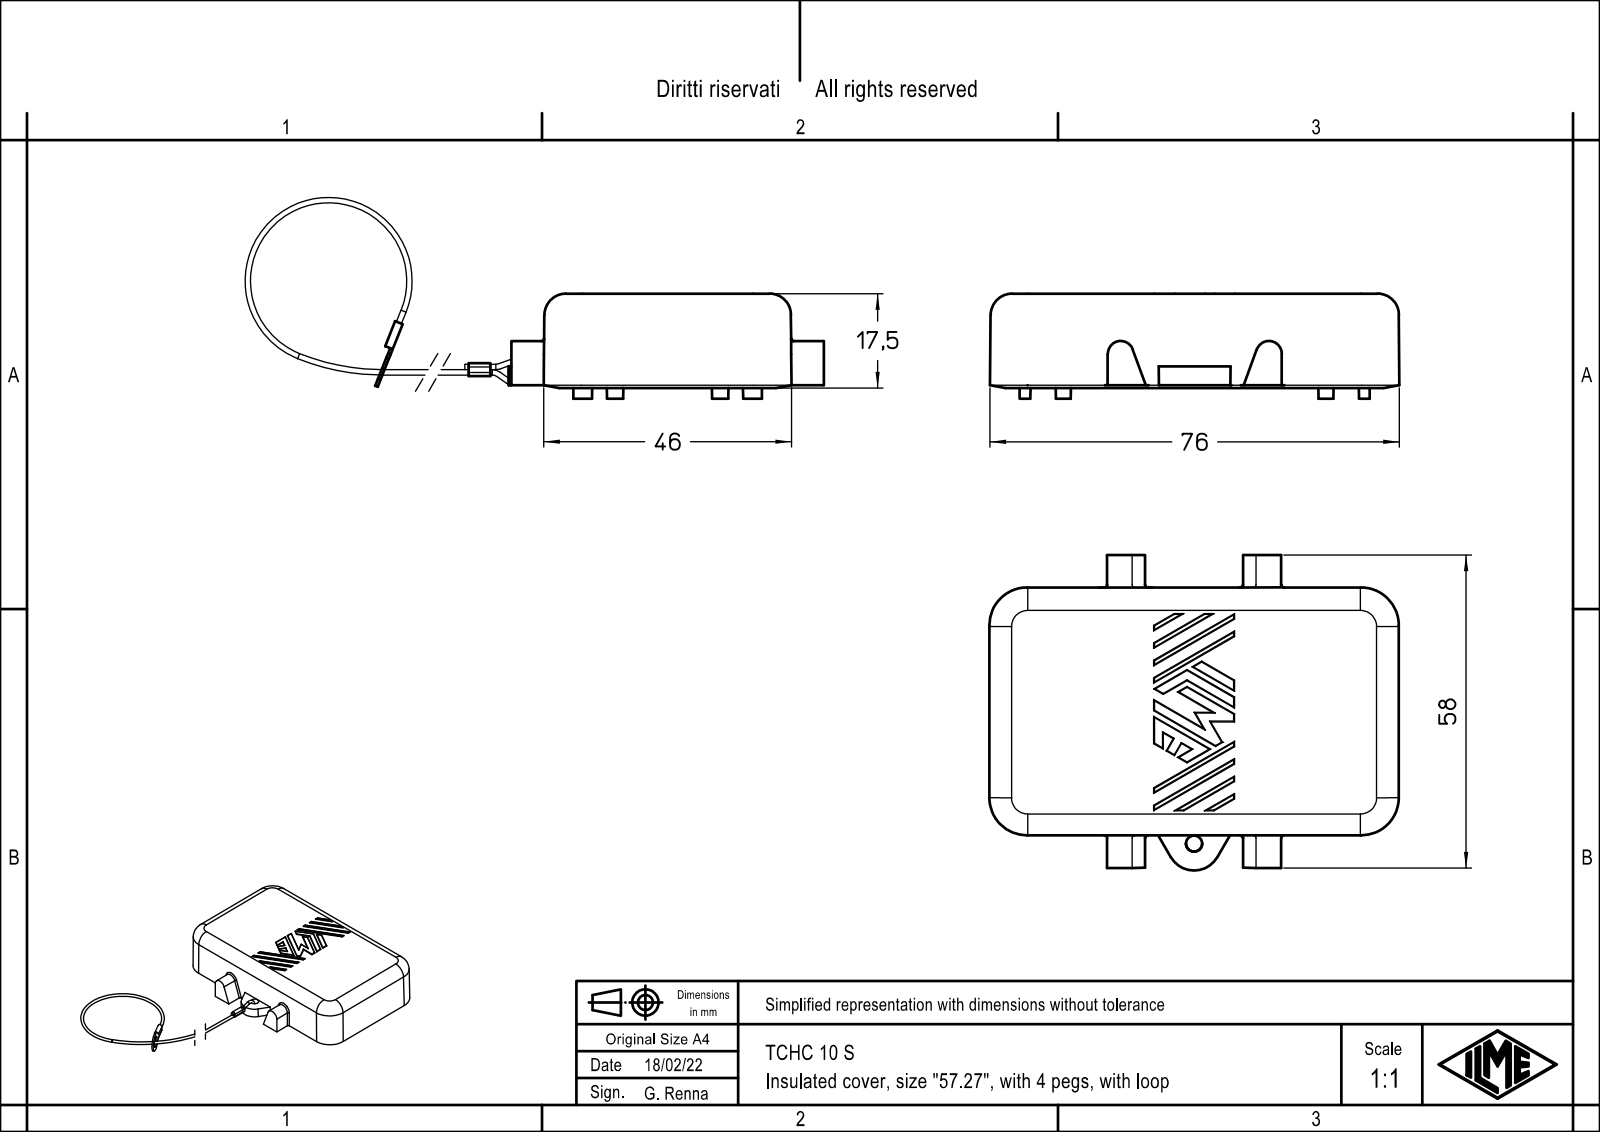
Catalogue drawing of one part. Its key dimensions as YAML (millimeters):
part_name: "TCHC_10_S"
step_written_by: "Creo Elements/Direct Modeling 20.1B 02-Apr-2019 (C) Parametric Technology GmbH (AUTOMOTIVE_DESIGN)"
units: millimeters
bodies: {solids: 1, faces: 281, planar: 116, cylindrical: 124, other: 41}
overall_size: [228.27, 81.38, 19.65]
volume: 34243
surface_area: 15246
round_holes:
  - {diameter: 3, count: 1}
  - {diameter: 4.2, count: 1}
round_bosses_or_shafts:
  - {diameter: 1, count: 5}
  - {diameter: 7, count: 1}
partial_cylinders:
  - {radius: 0.15, count: 44}
  - {radius: 1.5, count: 8}
  - {radius: 0.5, count: 4}
  - {radius: 4, count: 4}
  - {radius: 7, count: 4}
  - {radius: 0.7, count: 2}
  - {radius: 0.75, count: 2}
  - {radius: 1.25, count: 2}
face_to_face_distances: [5.5, 11.49, 16.99, 17.14, 5.65, 7, 6.99, 58, 19.5, 12.22]
